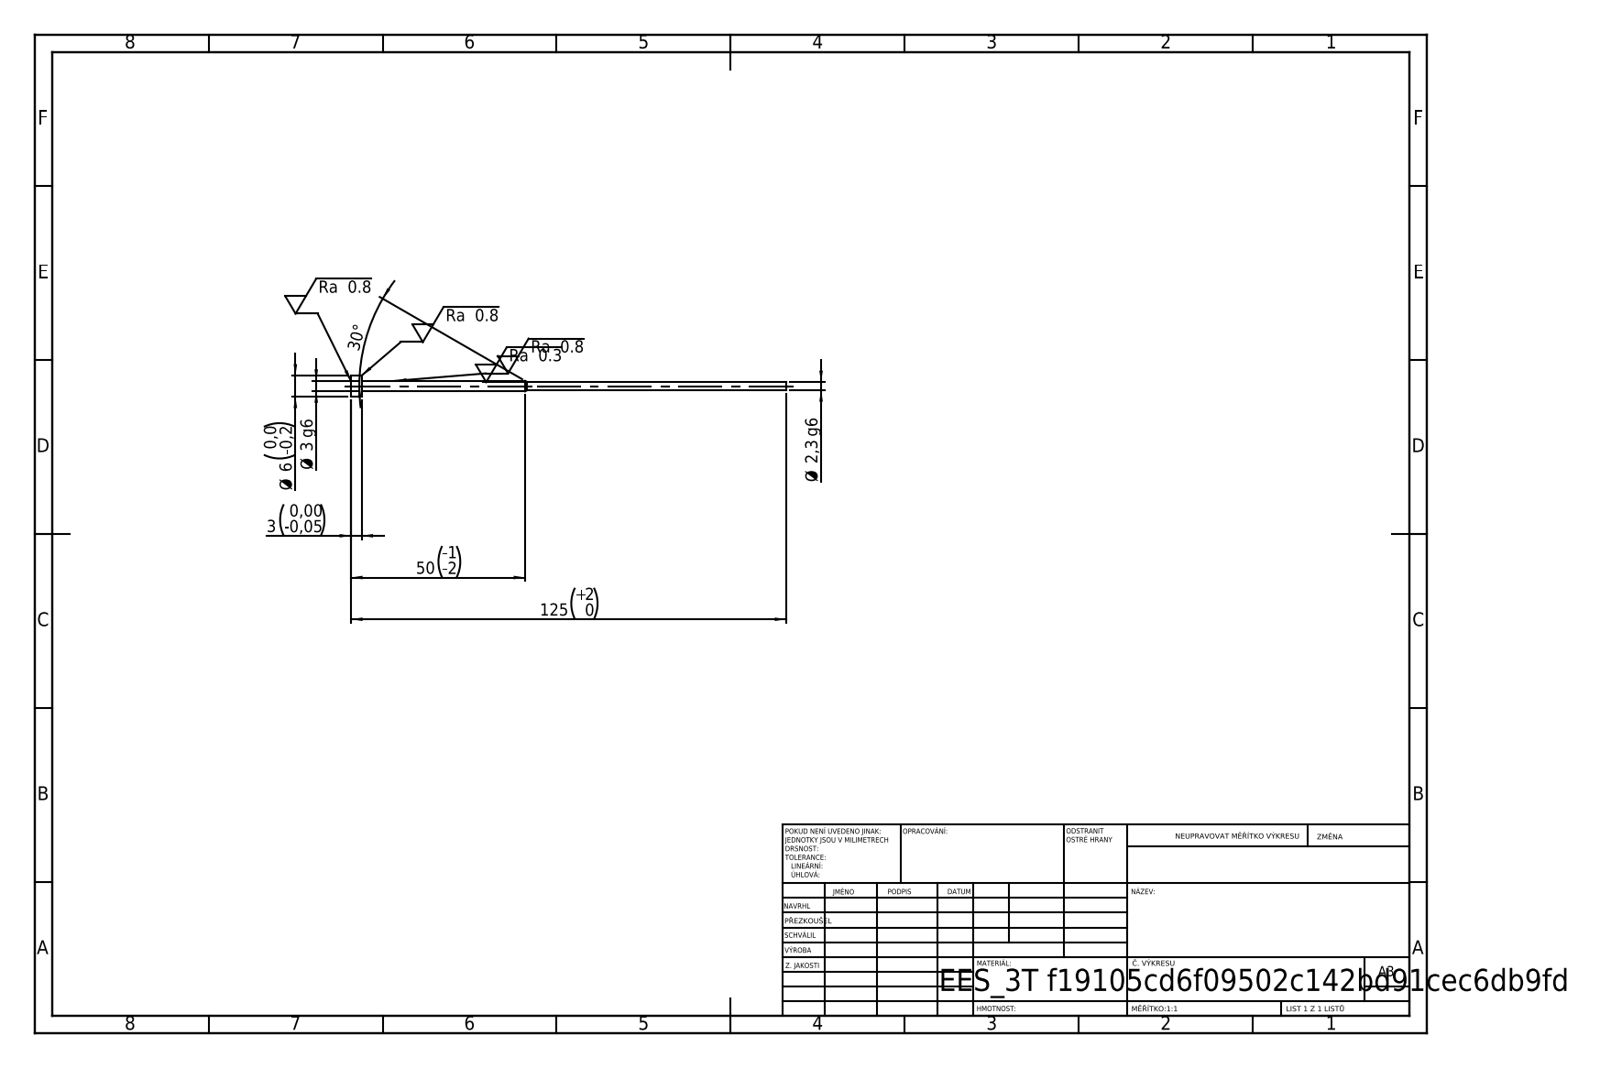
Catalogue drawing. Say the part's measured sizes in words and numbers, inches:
Its 3-D file was written by "SolidWorks 2019 (CONFIG_CONTROL_DESIGN)". It is 1 solid with 11 faces: 3 planar, 6 cylindrical and 2 other. Overall it measures 4.921 by 0.236 by 0.236 inches. Its volume is 0.044 cubic inches and its surface area 1.7 square inches. Round bosses or shafts: 1 of diameter 0.236, 1 of diameter 0.118, 1 of diameter 0.091. The main face-to-face distances are 0.118, 4.803, 4.921.
